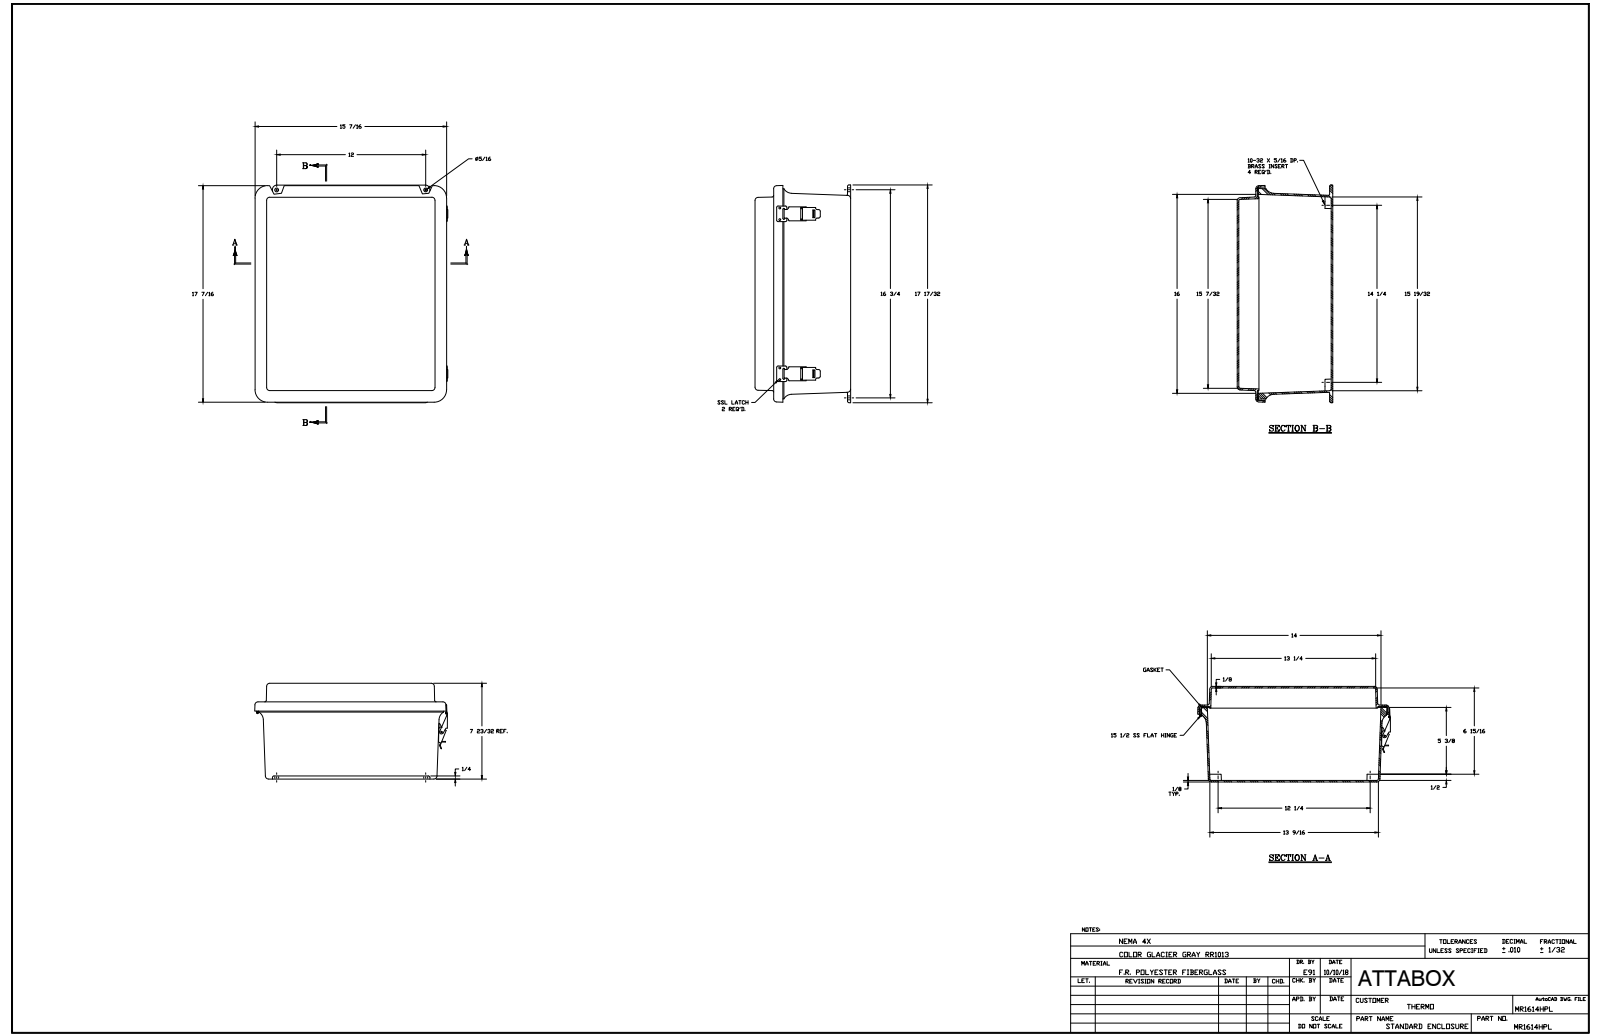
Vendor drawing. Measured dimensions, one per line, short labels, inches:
name: MR1614HPL
written by: SolidWorks 2018 (AUTOMOTIVE_DESIGN)
unit: in
bodies: 38 solids, 1141 faces (498 planar, 472 cylindrical, 171 other)
size: 17.531 × 15.566 × 7.697
volume: 147.4 in³; area: 2 133 in²
holes: 22× ⌀0.14, 10× ⌀0.131, 8× ⌀0.104, 8× ⌀0.152, 4× ⌀0.13, 4× ⌀0.156, 4× ⌀0.218, 2× ⌀0.135, 2× ⌀0.375, 1× ⌀0.085
bosses: 12× ⌀0.125, 8× ⌀0.25, 4× ⌀0.27, 4× ⌀0.125, 1× ⌀0.3, 1× ⌀0.17, 1× ⌀0.155, 1× ⌀0.135
rounds: 28× R0.125, 20× R0.015, 20× R0.031, 20× R0.25, 16× R0.045, 12× R0.03, 8× R0.023, 6× R0.06
face distances: 0.125, 0.125, 7.447, 7.697, 7.572, 7.572, 1.502, 5.945, 6.07, 1.627
hole spacings: 3.75, 7.5, 12.869, 0.937, 12.868, 0.25, 0.75, 11.25
